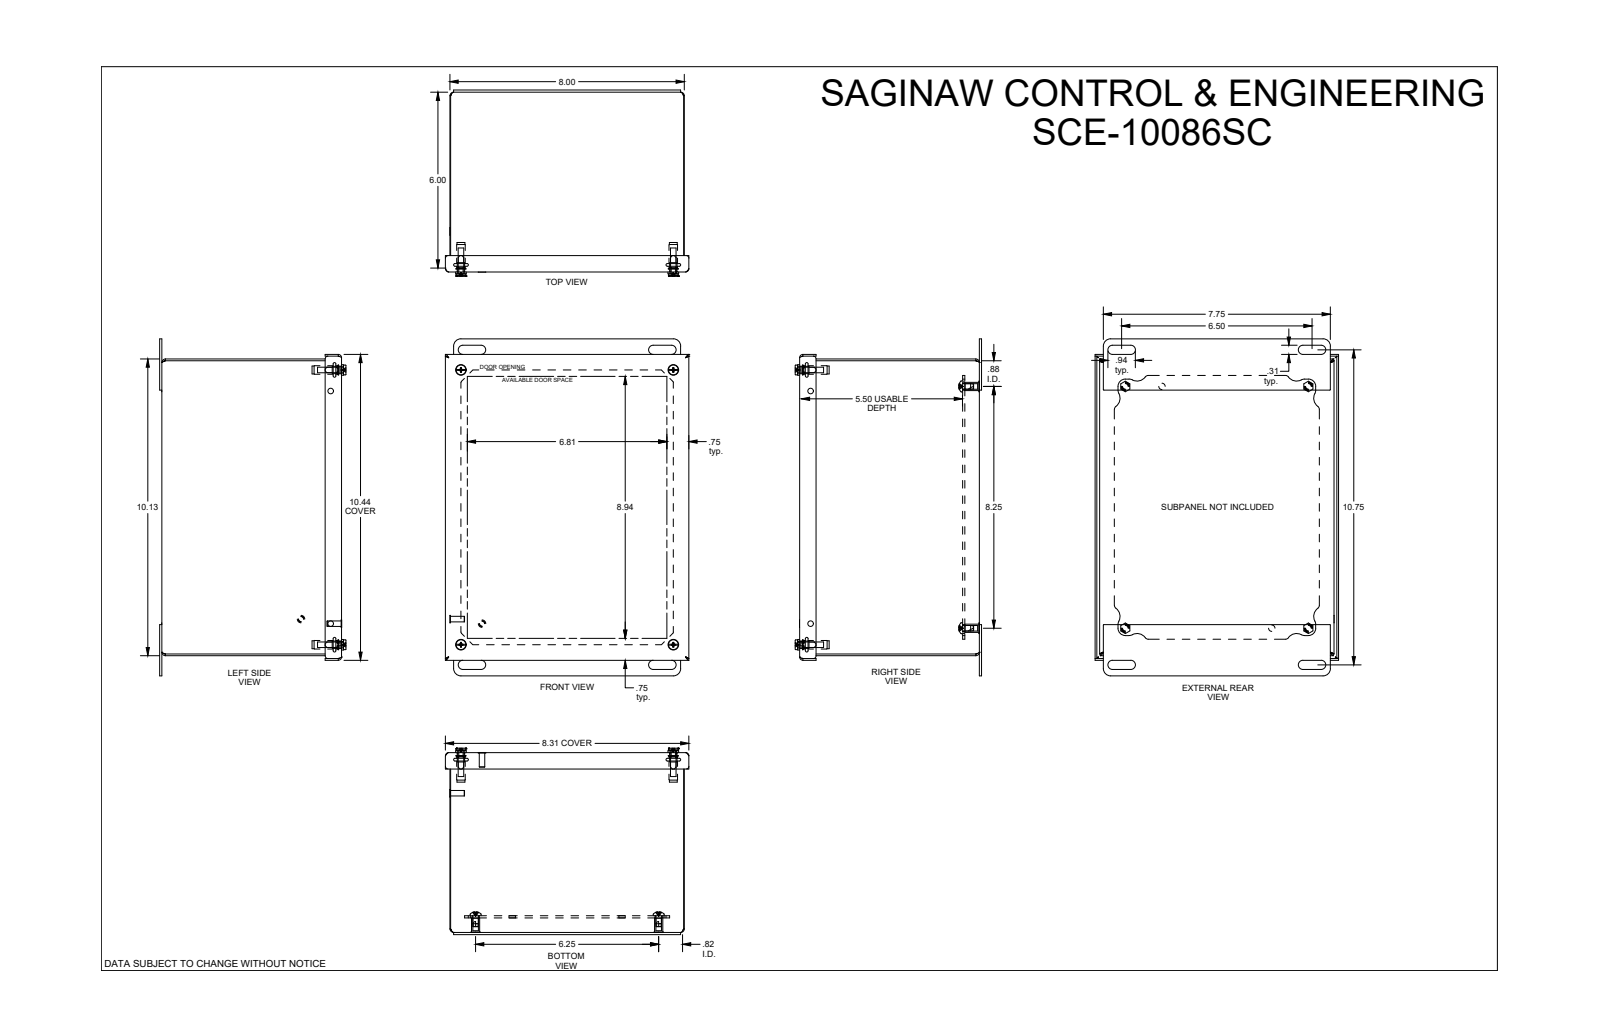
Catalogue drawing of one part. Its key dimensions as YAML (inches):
part_name: "SCE-10086SC"
step_written_by: "SolidWorks 2019 (AUTOMOTIVE_DESIGN)"
units: inches
bodies: {solids: 28, faces: 773, planar: 328, cylindrical: 183, other: 262}
overall_size: [11.5, 8.313, 6.361]
volume: 32.43
surface_area: 1045
round_holes:
  - {diameter: 0.19, count: 8}
  - {diameter: 0.25, count: 8}
  - {diameter: 0.22, count: 4}
  - {diameter: 0.266, count: 4}
  - {diameter: 0.281, count: 4}
  - {diameter: 0.317, count: 4}
  - {diameter: 0.218, count: 2}
  - {diameter: 0.193, count: 1}
round_bosses_or_shafts:
  - {diameter: 0.188, count: 10}
  - {diameter: 0.437, count: 4}
  - {diameter: 0.373, count: 4}
  - {diameter: 0.362, count: 4}
  - {diameter: 0.34, count: 4}
  - {diameter: 0.334, count: 4}
  - {diameter: 0.292, count: 4}
  - {diameter: 0.28, count: 4}
partial_cylinders:
  - {radius: 0.05, count: 20}
  - {radius: 0.125, count: 16}
  - {radius: 0.25, count: 16}
  - {radius: 0.005, count: 8}
  - {radius: 0.156, count: 8}
  - {radius: 0.255, count: 8}
  - {radius: 0.344, count: 8}
  - {radius: 0.02, count: 4}
face_to_face_distances: [0.06, 6.075, 7.94, 10.065, 6.135, 6.015, 5.505, 0.075, 0.57, 0.51]
hole_center_spacings: [8.827, 0.753, 6.773, 11.101, 8.25, 8.826, 9.375, 9.375]
